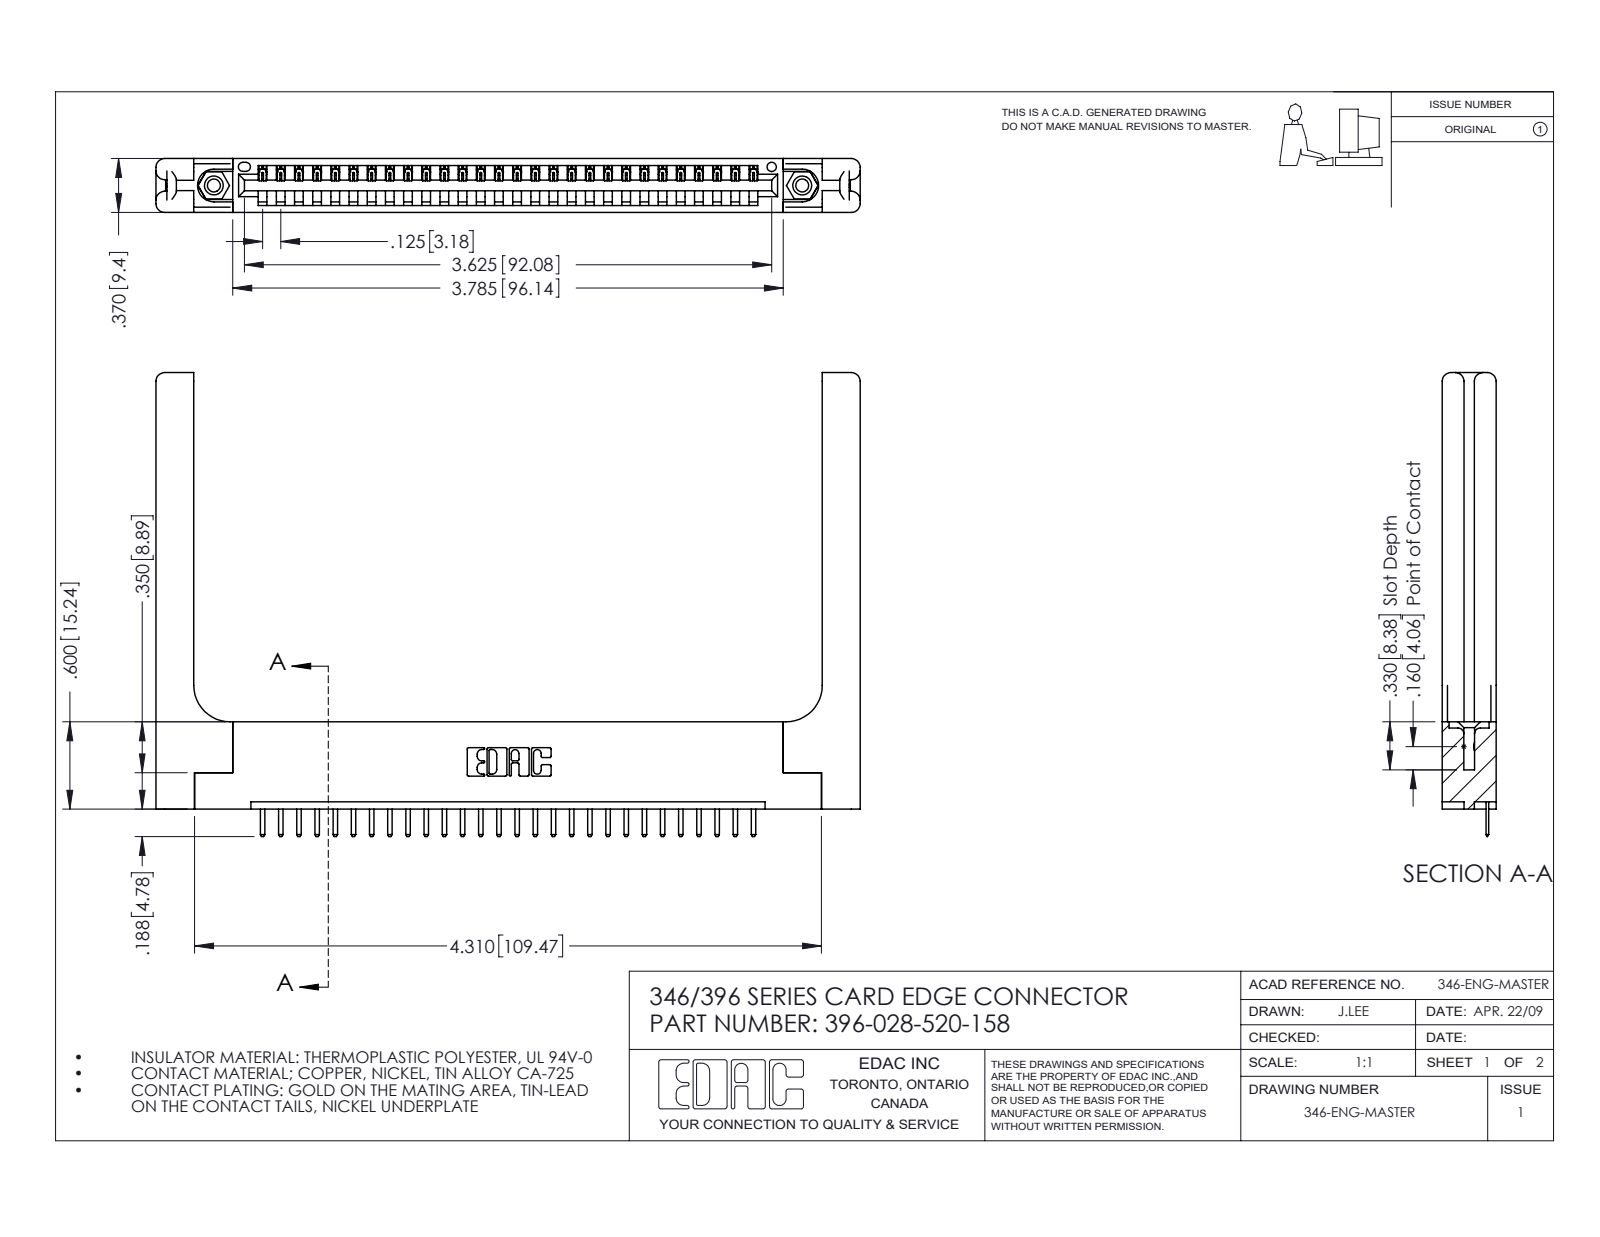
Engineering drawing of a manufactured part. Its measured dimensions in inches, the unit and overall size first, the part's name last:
Units: inches
Overall size (bounding box): 4.841 × 3.188 × 0.37
Round holes (diameter × count): ⌀0.089 ×2, ⌀0.125 ×2, ⌀0.156 ×2, ⌀0.064 ×1
Round bosses / shafts (diameter × count): ⌀0.155 ×2
Partial cylindrical surfaces — rounded edges, fillets, slot ends (radius × count): R0.01 ×58, R0.006 ×56, R0.01 ×22, R0.06 ×16, R0.007 ×6, R0.031 ×6, R0.026 ×3, R0.03 ×2
Main face-to-face distances: 0.37, 0.072, 0.148, 0.048, 0.322, 0.15, 0.25, 0.298, 0.025, 0.076
Hole centre spacings: 0.246, 3.837, 4.045
Volume: 1.166 in³ · Surface area: 29.82 in²
Bodies: 33 solids, 2114 faces (1400 planar, 654 cylindrical, 60 other)
Part name (STEP PRODUCT): 346-220-058_345-220-058; 345-292-001_345-293-120; 345-250-001_345-250-001-102; 396-028-520-158 (+1 more)
STEP written by: SolidWorks 2016 (CONFIG_CONTROL_DESIGN)
